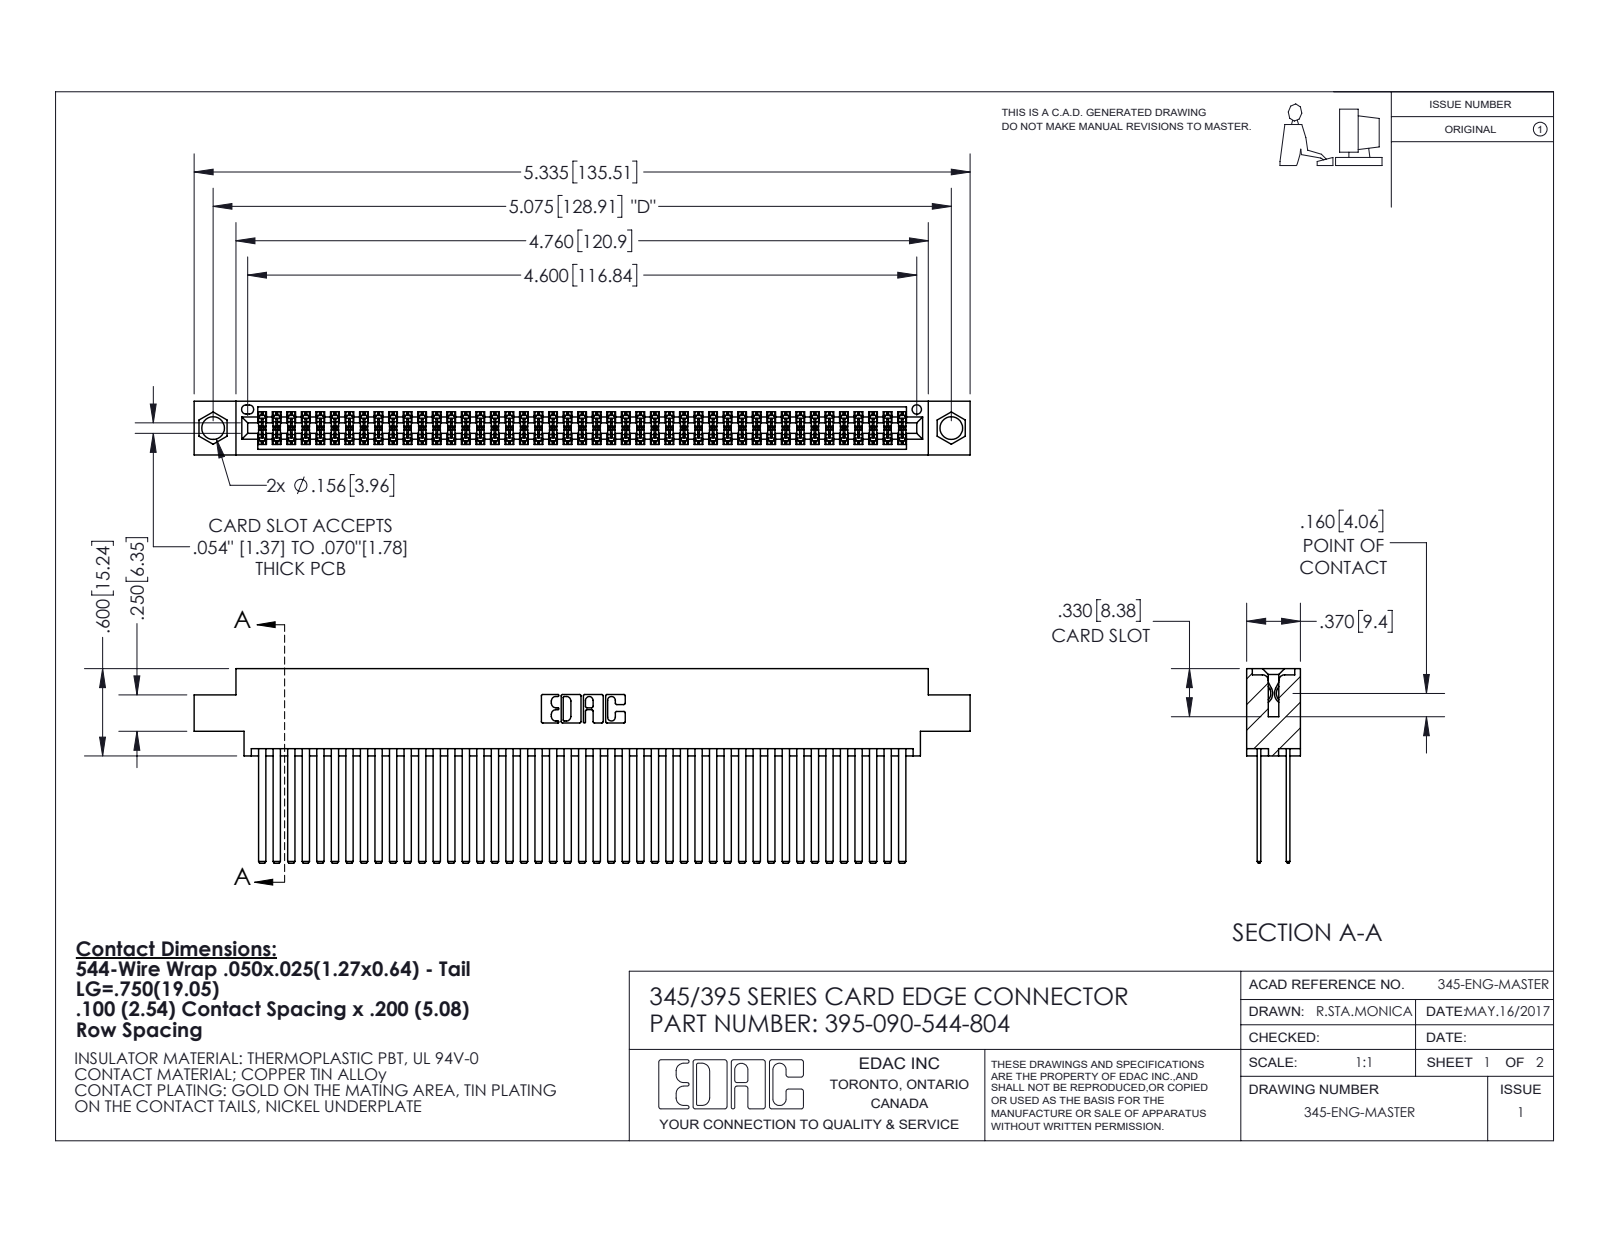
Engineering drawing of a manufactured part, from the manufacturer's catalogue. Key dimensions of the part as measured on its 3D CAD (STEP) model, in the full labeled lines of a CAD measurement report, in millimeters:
Part name (STEP PRODUCT): 395-090-544-804; 345 Part_0.170 Offset - 0.156 Dia-TI; 345-292-001_345-293-144
STEP written by: SolidWorks 2020 (CONFIG_CONTROL_DESIGN)
Units: millimetres
Bodies: 91 solids, 4104 faces (2708 planar, 1396 cylindrical, 0 other)
Overall size (bounding box): 135.5 × 34 × 9.4
Volume: 14 200 mm³ · Surface area: 24 790 mm²
Round holes (diameter × count): ⌀4 ×2, ⌀1.6 ×1
Partial cylindrical surfaces — rounded edges, fillets, slot ends (radius × count): R0.2 ×135, R0.3 ×22, R0.2 ×6, R0.8 ×6, R0.7 ×3, R0.4 ×2, R0.5 ×2, R0.6 ×2
Main face-to-face distances: 5.1, 0.6, 1.8, 2.5, 6.9, 7.6, 5.7, 4.4, 9.4, 3.8
Hole centre spacings: 6.9, 122.9, 128.9
